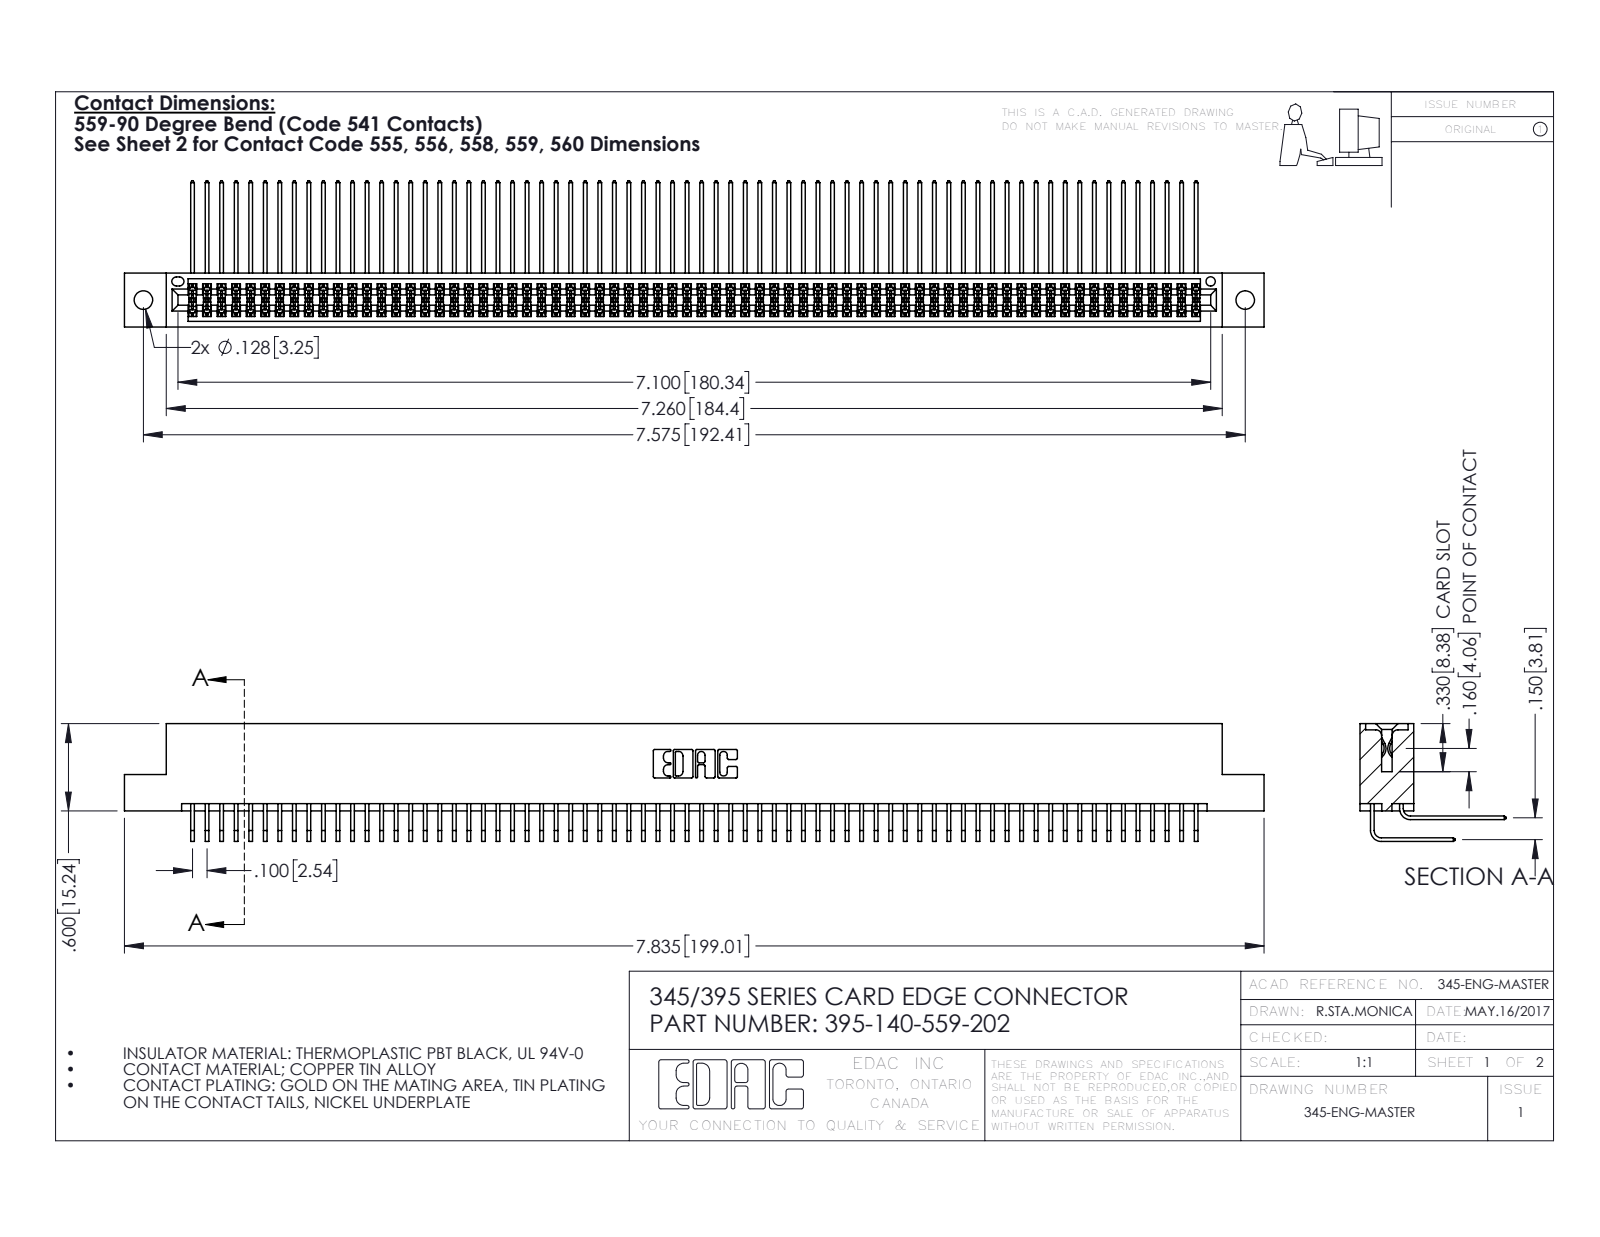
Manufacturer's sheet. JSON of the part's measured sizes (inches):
{"part_name": "345 Part_Flush Mounting Lugs - 0.128 Dia; 345-292-001_558 559 Tail - 1; 395-140-559-202; 345-292-001_559 Tail - 2", "step_written_by": "SolidWorks 2016 (CONFIG_CONTROL_DESIGN)", "units": "inches", "bodies": {"solids": 141, "faces": 7406, "planar": 4980, "cylindrical": 2426, "other": 0}, "overall_size": [7.835, 1.005, 0.809], "volume_in3": 1.243, "surface_area_in2": 52.96, "round_holes": [[0.128, 2], [0.064, 1]], "partial_cylinders_radius": [[0.006, 279], [0.01, 22], [0.007, 6], [0.031, 6], [0.026, 3], [0.014, 2], [0.019, 2], [0.022, 2]], "face_to_face_distances": [0.072, 0.298, 0.2, 0.37, 0.098, 0.272, 0.025, 0.225, 0.175, 0.15], "hole_center_spacings": [0.27, 7.339, 7.575]}
